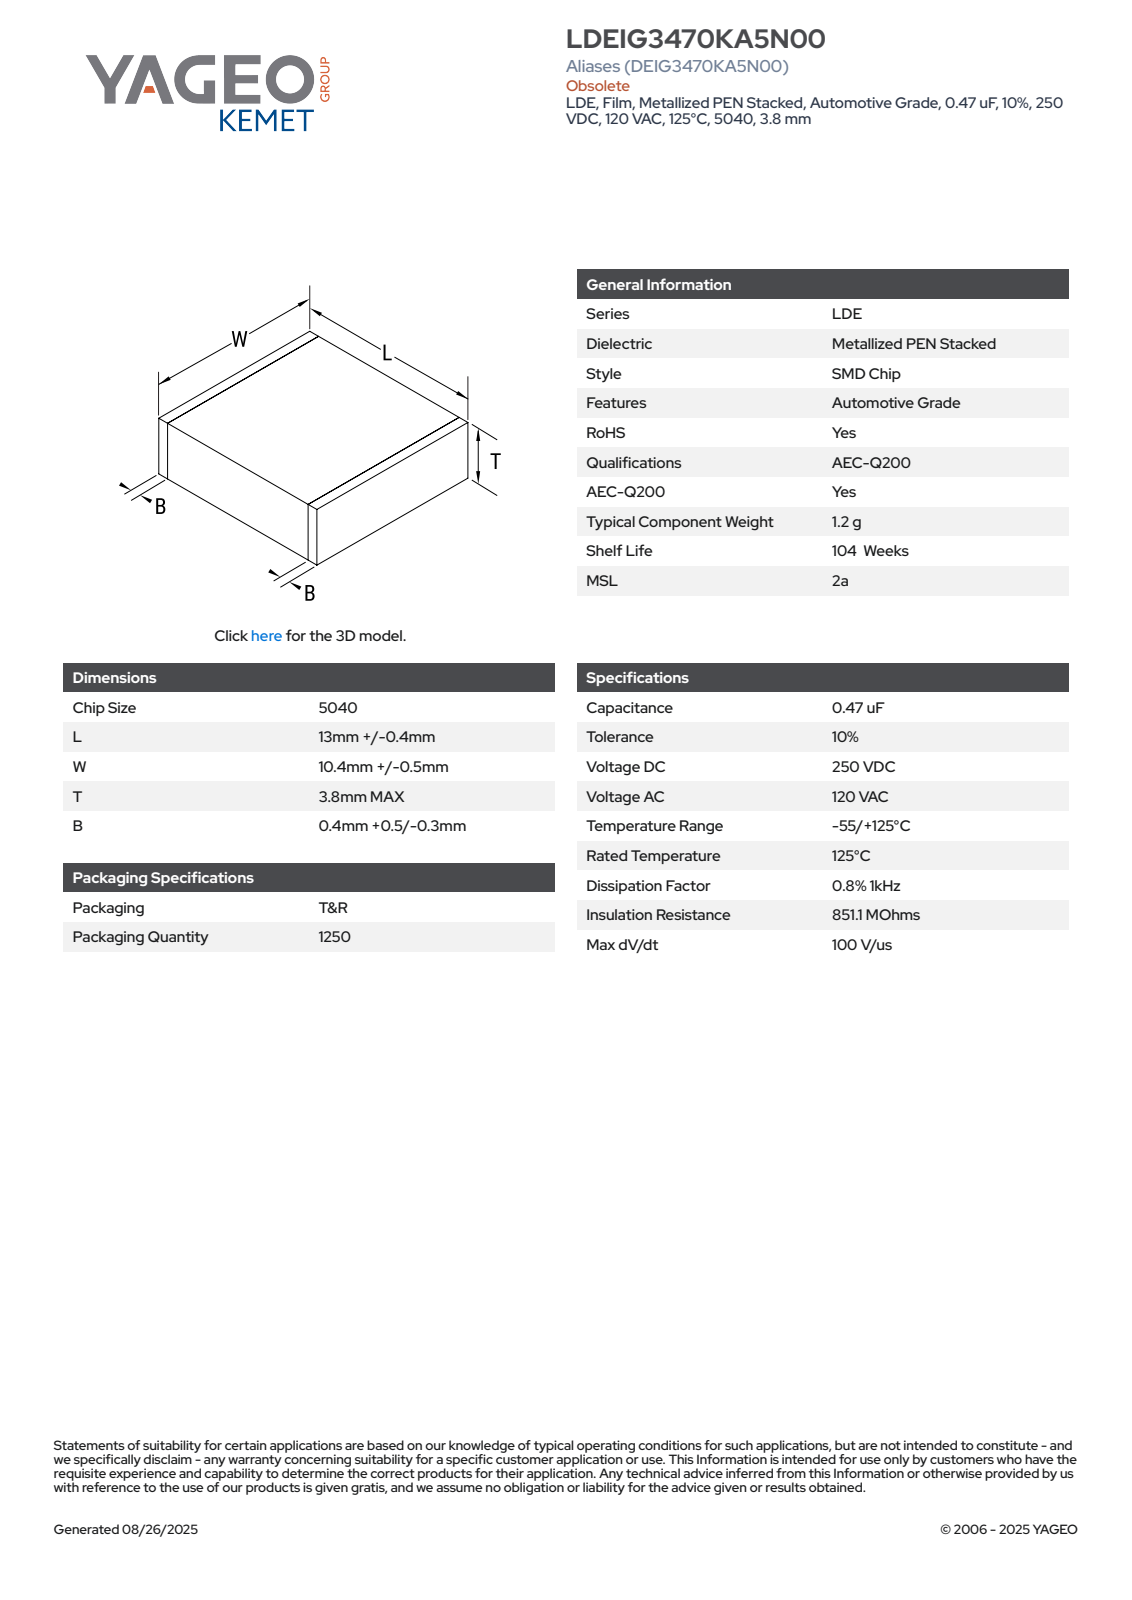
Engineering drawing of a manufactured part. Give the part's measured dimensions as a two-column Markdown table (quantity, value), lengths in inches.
| quantity | value |
| --- | --- |
| part name | CFS_LDELDB_5040_L13.4W10.9T3.8B0.9 |
| STEP written by | SolidWorks 2020 (AUTOMOTIVE_DESIGN) |
| units | inches |
| bodies | 4 solids, 73 faces (73 planar, 0 cylindrical, 0 other) |
| overall size | 0.528 × 0.429 × 0.15 |
| volume | 0.034 in³ |
| surface area | 0.752 in² |
| main face-to-face distances | 0.149, 0.428, 0.528, 0.149, 0.15, 0.429, 0.429, 0.02, 0.508, 0.488 |
